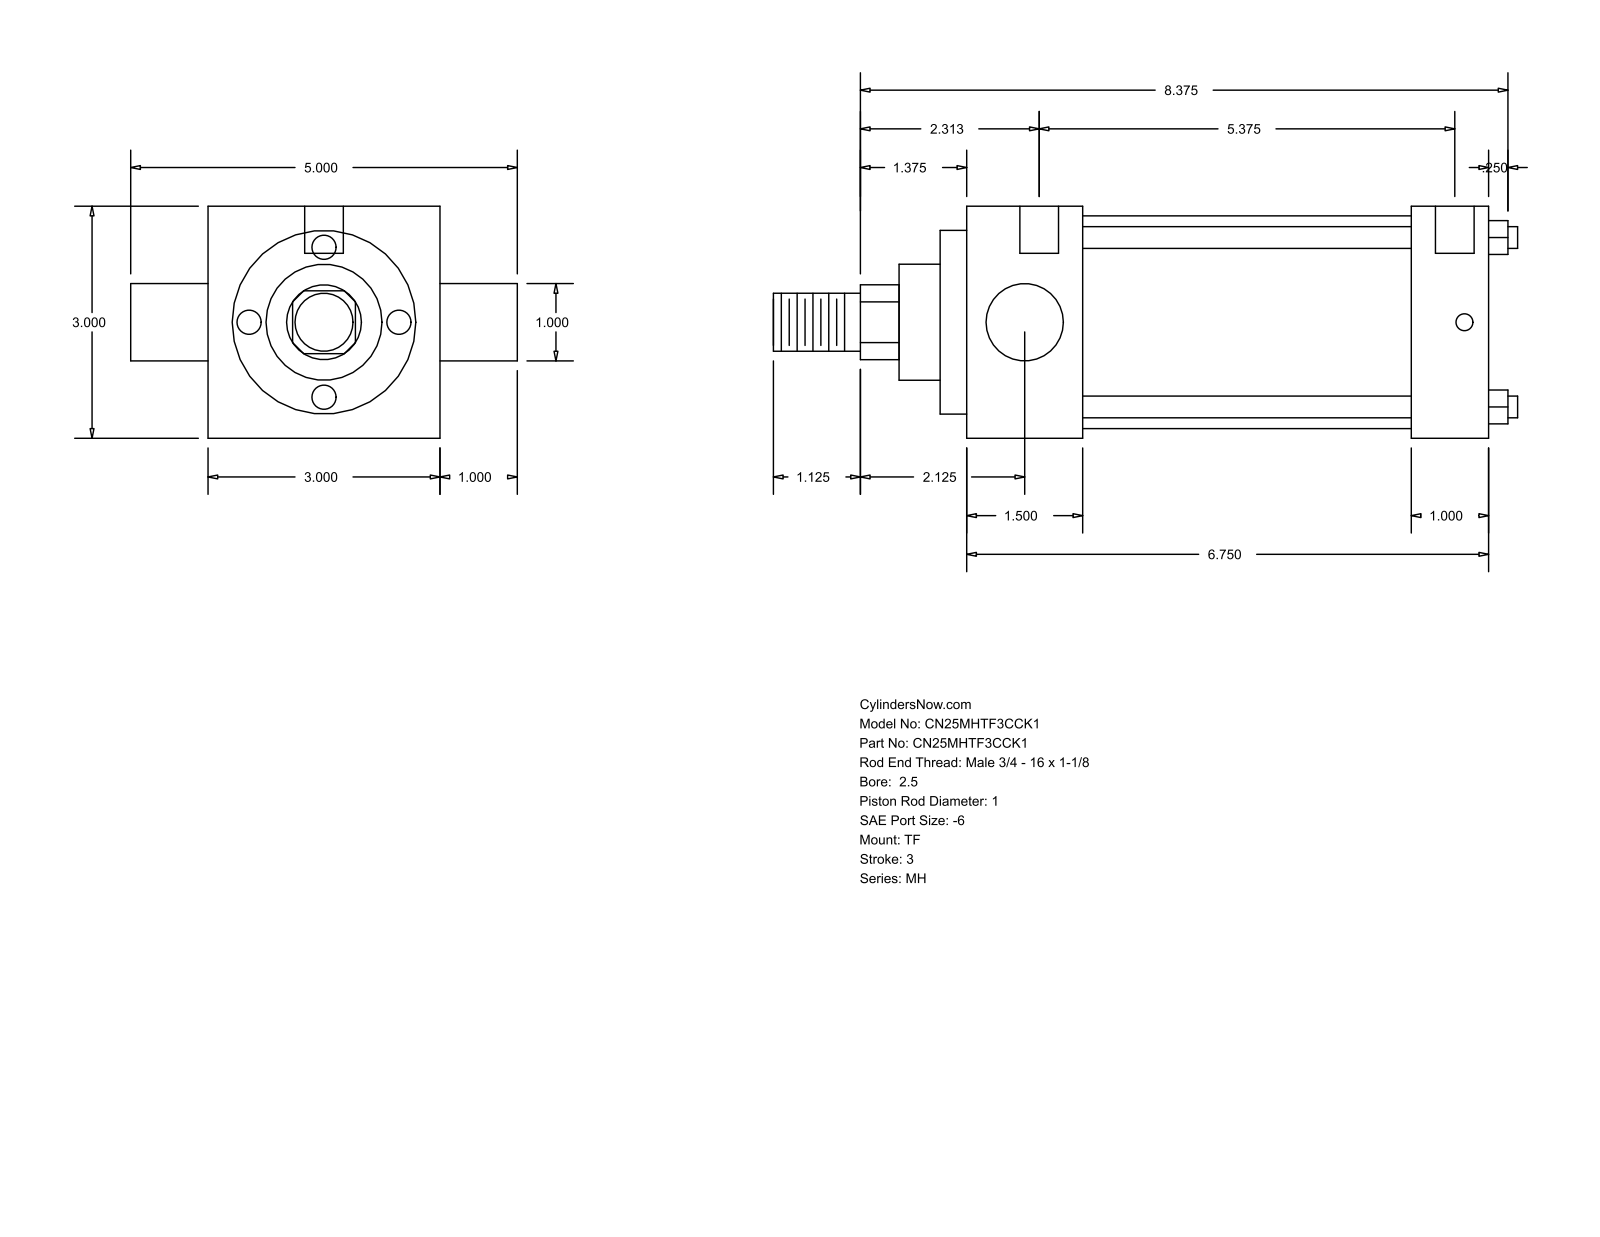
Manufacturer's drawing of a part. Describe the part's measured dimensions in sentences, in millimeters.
The part is named "MH_TF__0250_1". Its 3-D file was written by "GSSL Pune (CONFIG_CONTROL_DESIGN)". It is 0 solids with 86 faces: 61 planar, 25 cylindrical and 0 other. Overall it measures 244.47 by 127 by 76.2 millimeters. Round holes: 3 of diameter 5.56, 2 of diameter 12.7. Round bosses or shafts: 4 of diameter 7.14, 2 of diameter 25.4, 1 of diameter 69.85, 1 of diameter 60.33, 1 of diameter 38.1, 1 of diameter 19.05. Partial cylindrical surfaces (rounded edges, fillets, slot ends): 1 of radius 12.29. The main face-to-face distances are 76.2, 171.46, 38.11, 133.35, 146.05, 107.94, 25.41, 8.73, 46.84, 154.78. The hole center spacings are 3.18, 4.76, 136.52, 139.7, 141.28, 144.46.
